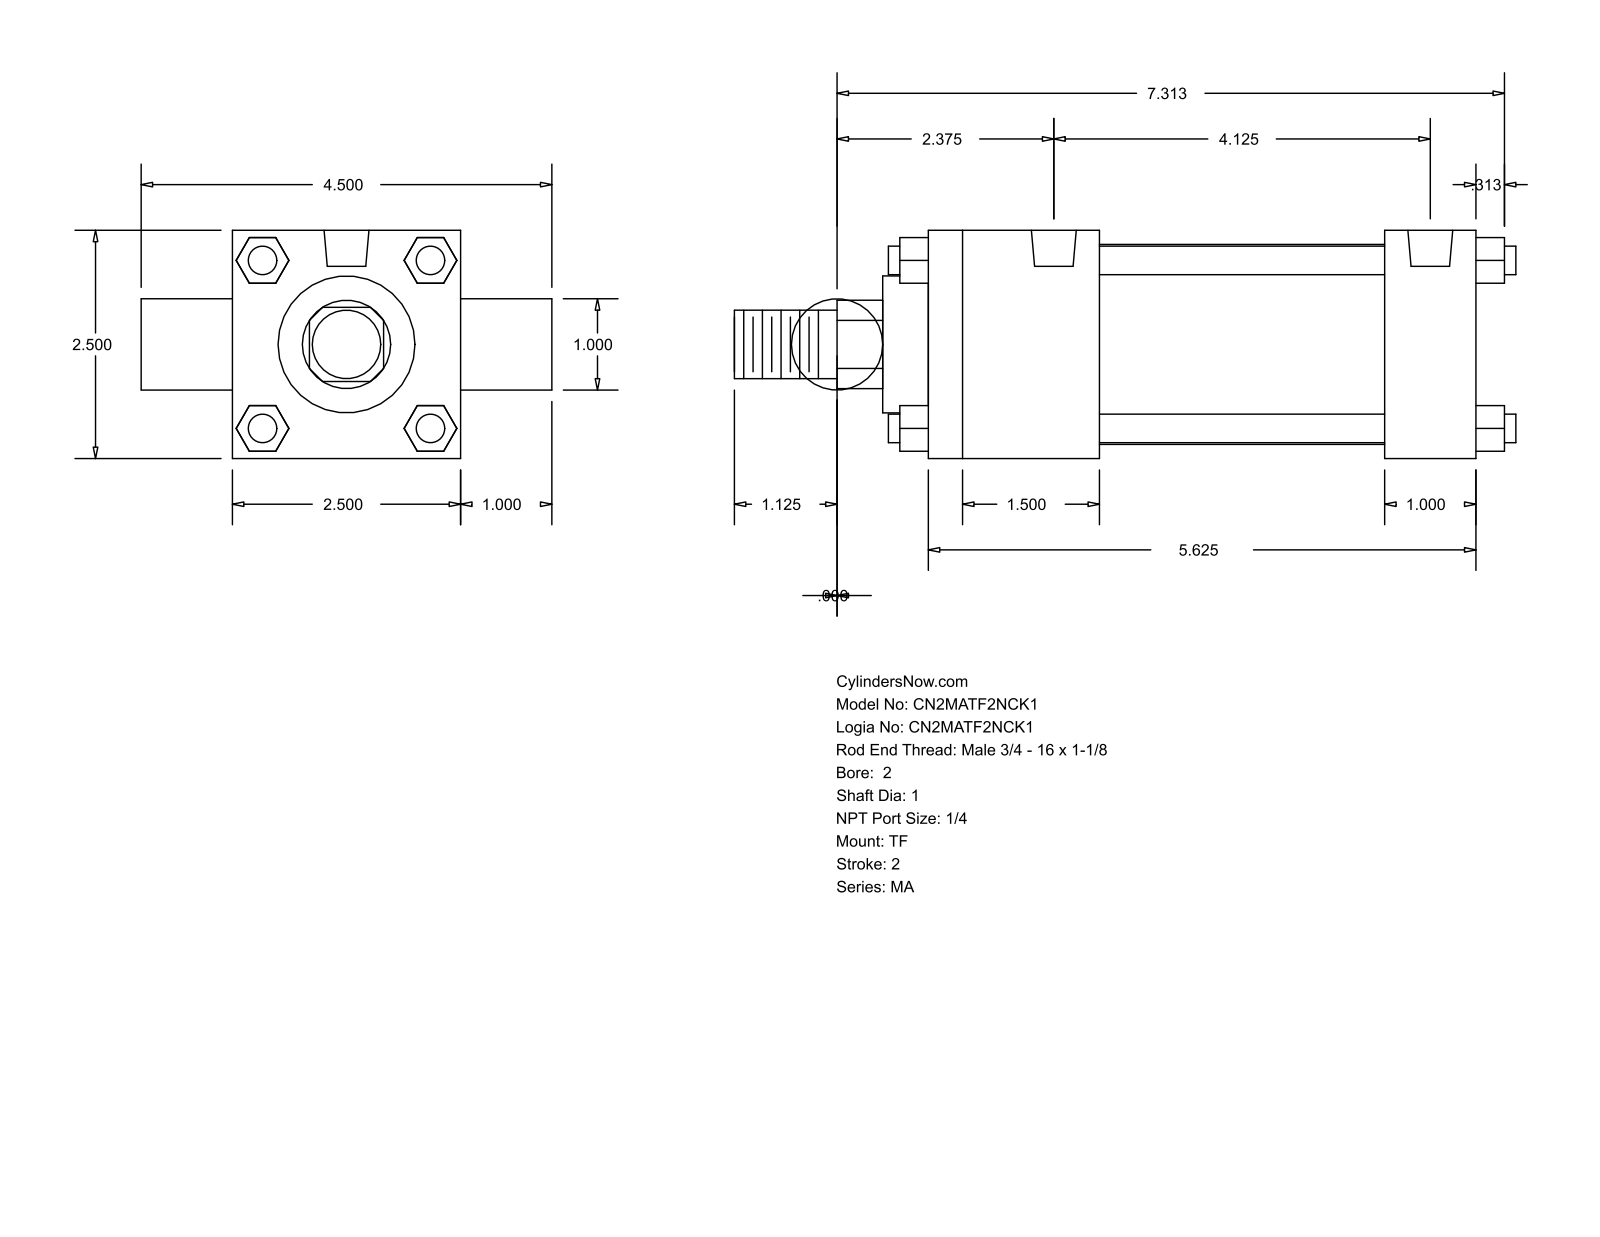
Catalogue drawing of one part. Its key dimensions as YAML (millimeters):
part_name: "MA_TF__0200_1"
step_written_by: "GSSL Pune (CONFIG_CONTROL_DESIGN)"
units: millimeters
bodies: {solids: 0, faces: 120, planar: 92, cylindrical: 28, other: 0}
overall_size: [217.49, 114.3, 63.5]
round_holes:
  - {diameter: 7.94, count: 3}
  - {diameter: 12.49, count: 2}
round_bosses_or_shafts:
  - {diameter: 7.94, count: 4}
  - {diameter: 25.4, count: 2}
  - {diameter: 55.63, count: 1}
  - {diameter: 38.1, count: 1}
  - {diameter: 19.05, count: 1}
partial_cylinders:
  - {radius: 12.29, count: 1}
face_to_face_distances: [63.5, 25.4, 152.4, 12.7, 47.63, 127, 79.37, 104.77, 88.9, 23.37]
hole_center_spacings: [104.77]
